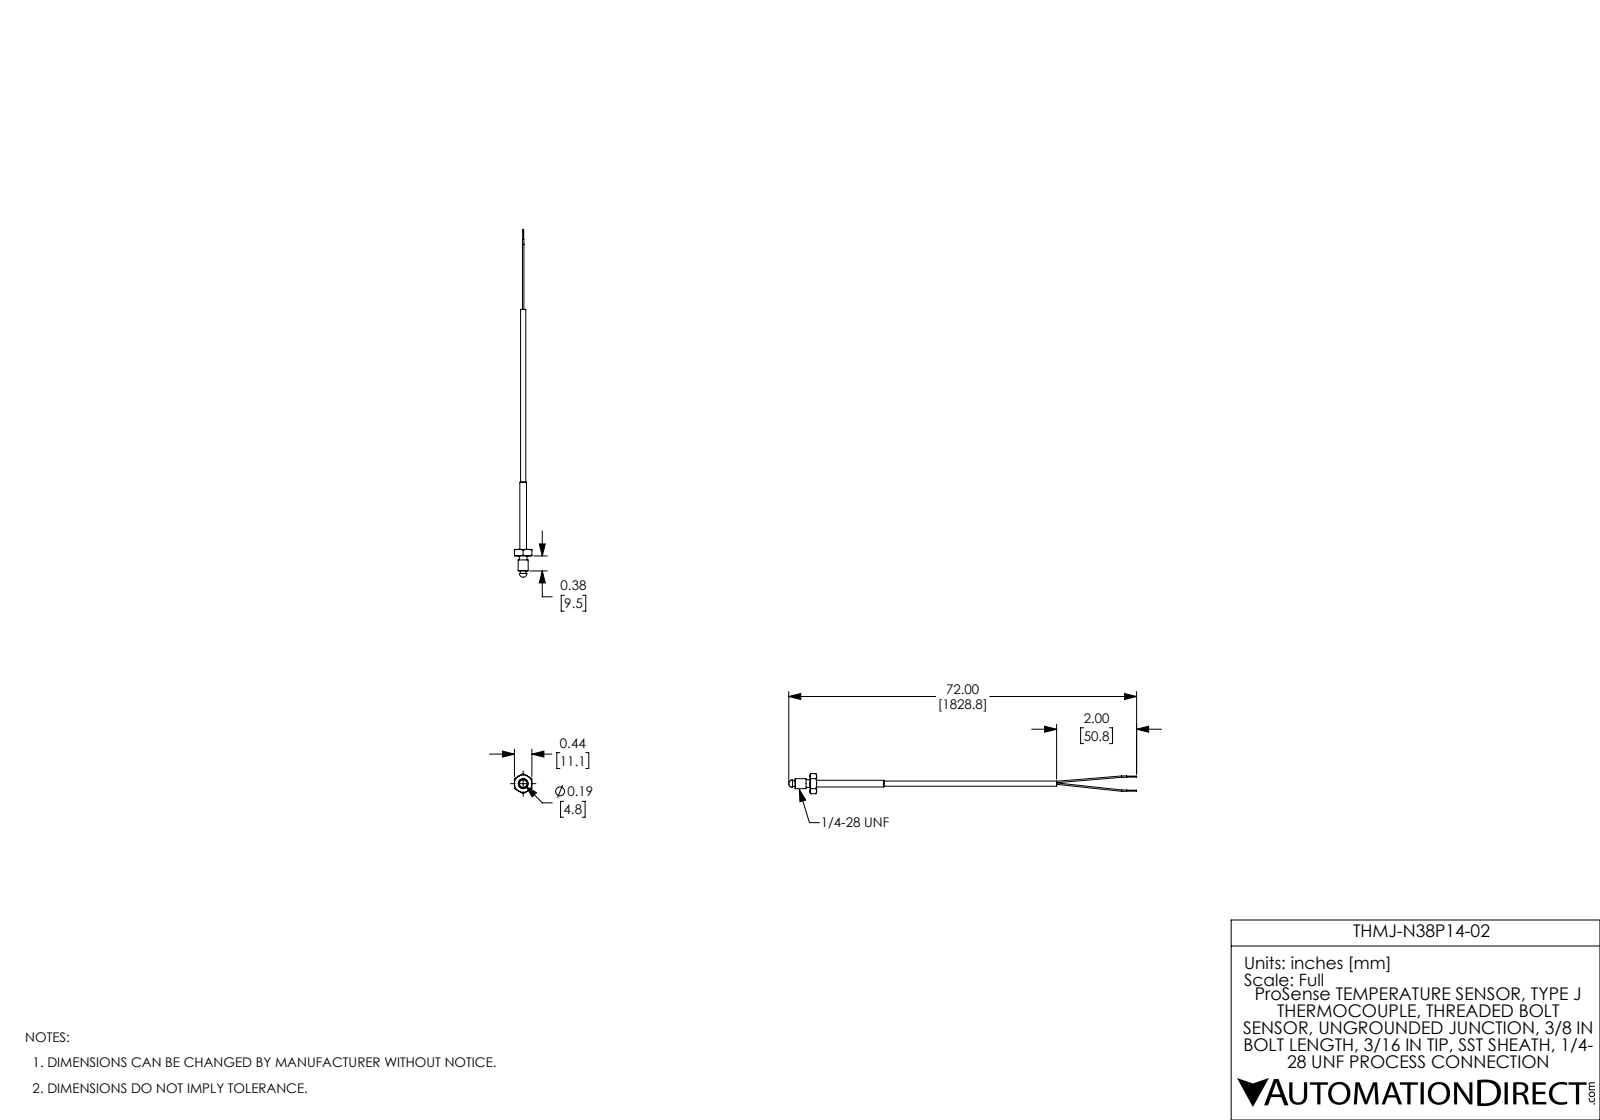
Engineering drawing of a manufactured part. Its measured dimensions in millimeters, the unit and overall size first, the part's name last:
Units: millimetres
Overall size (bounding box): 220.9 × 12.8 × 11.1
Round bosses / shafts (diameter × count): ⌀0.6 ×2, ⌀6.4 ×1, ⌀4.9 ×1, ⌀4.3 ×1, ⌀3.6 ×1, ⌀3.3 ×1, ⌀0.9 ×1, ⌀0.9 ×1
Main face-to-face distances: 4.2, 11, 13.7, 9.5, 6.7, 2.5, 7, 15.3, 11.1, 8.6
Volume: 2 360 mm³ · Surface area: 2 596 mm²
Bodies: 1 solid, 57 faces (17 planar, 18 cylindrical, 22 other)
Part name (STEP PRODUCT): THMJ-N38P14-02
STEP written by: SolidWorks 2017 (AUTOMOTIVE_DESIGN)
